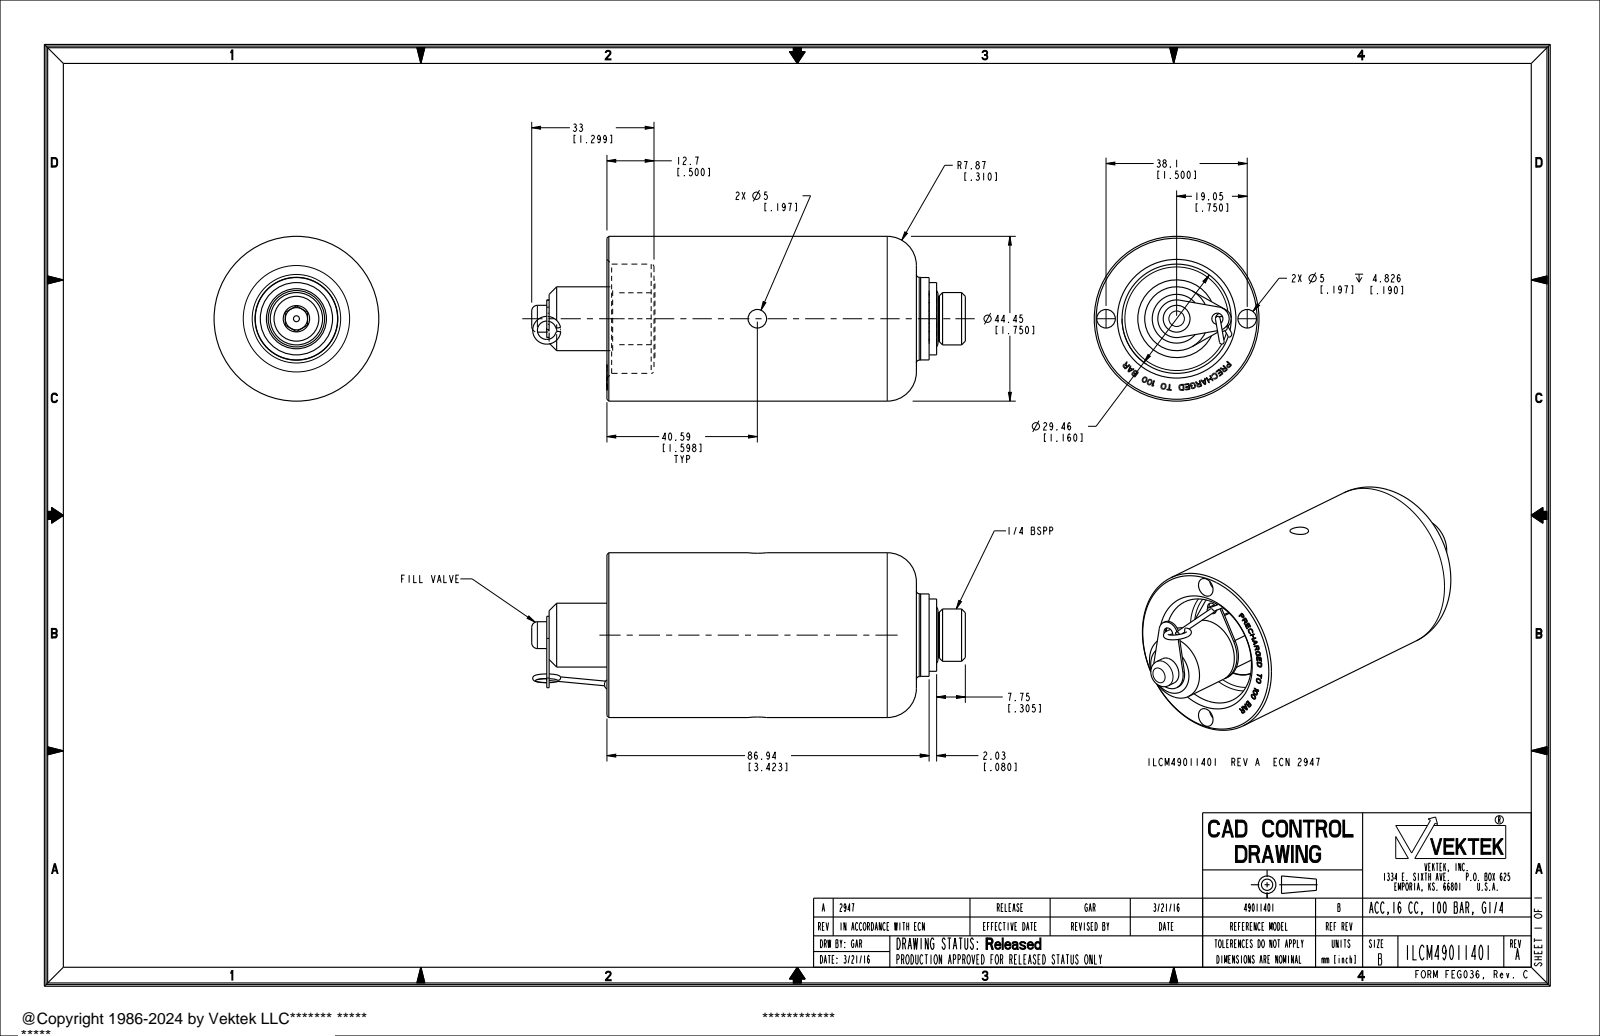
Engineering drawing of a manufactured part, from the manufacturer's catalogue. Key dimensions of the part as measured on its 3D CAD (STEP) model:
Part name (STEP PRODUCT): ILCM49011401
STEP written by: PRO/ENGINEER BY PARAMETRIC TECHNOLOGY CORPORATION, 2013320 (AUTOMOTIVE_DESIGN)
Units: inches
Bodies: 1 solid, 778 faces (565 planar, 92 cylindrical, 121 other)
Overall size (bounding box): 4.607 × 1.75 × 1.75
Volume: 6.193 in³ · Surface area: 53.64 in²
Round holes (diameter × count): ⌀0.197 ×3, ⌀0.118 ×2, ⌀0.063 ×1, ⌀0.12 ×1, ⌀0.236 ×1, ⌀0.392 ×1, ⌀0.442 ×1, ⌀0.498 ×1, ⌀0.515 ×1, ⌀0.541 ×1, ⌀0.638 ×1, ⌀0.825 ×1
Round bosses / shafts (diameter × count): ⌀1.75 ×1, ⌀1.248 ×1, ⌀1.229 ×1, ⌀1.004 ×1, ⌀1.003 ×1, ⌀0.88 ×1, ⌀0.875 ×1, ⌀0.768 ×1
Partial cylindrical surfaces — rounded edges, fillets, slot ends (radius × count): R0.015 ×2, R0.108 ×1, R0.125 ×1, R0.2 ×1
Main face-to-face distances: 1.113, 0.335, 0.545, 2.923, 0.5, 0.395, 1.14, 2.253, 0.485, 0.12
Hole centre spacings: 0.75, 0.039, 0.278, 0.317, 0.433, 0.472, 1.183, 1.222
